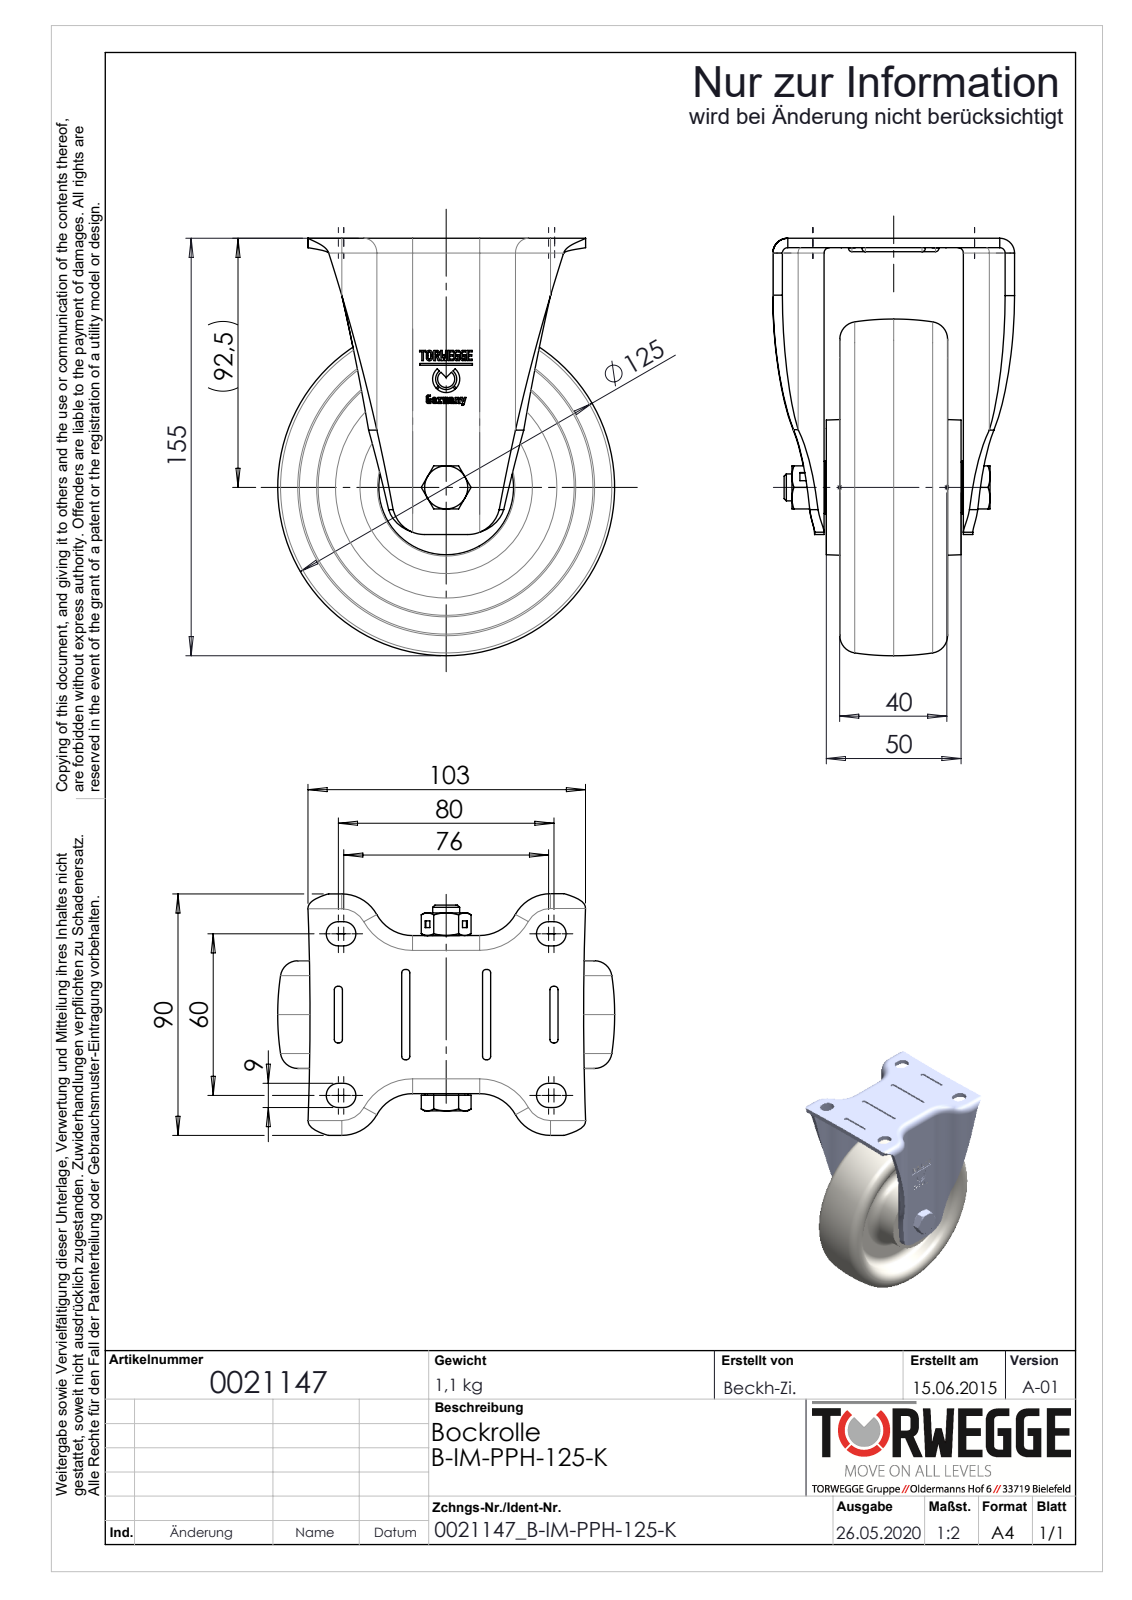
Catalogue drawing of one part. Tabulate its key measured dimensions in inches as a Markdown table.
| quantity | value |
| --- | --- |
| part name | 0021147 |
| STEP written by | SolidWorks 2018 (AUTOMOTIVE_DESIGN) |
| units | inches |
| bodies | 16 solids, 738 faces (341 planar, 223 cylindrical, 174 other) |
| overall size | 6.102 × 4.921 × 3.533 |
| volume | 24.66 in³ |
| surface area | 186.3 in² |
| round holes (diameter × count) | 0.335 × 1, 0.394 × 1, 0.402 × 1, 0.407 × 1, 0.591 × 1, 0.799 × 1, 1.121 × 1, 1.169 × 1, 1.181 × 1 |
| round bosses / shafts (diameter × count) | 1.378 × 1, 0.847 × 1, 0.778 × 1, 0.63 × 1, 0.587 × 1 |
| partial cylindrical surfaces (radius × count) | 0.049 × 20, 0.015 × 8, 0.138 × 8, 0.177 × 8, 0.008 × 7, 0.024 × 7, 0.079 × 5, 0.217 × 5 |
| main face-to-face distances | 0.138, 1.181, 0.787, 1.535, 0.959, 1.352, 0.821, 0.394, 1.215, 0.433 |
